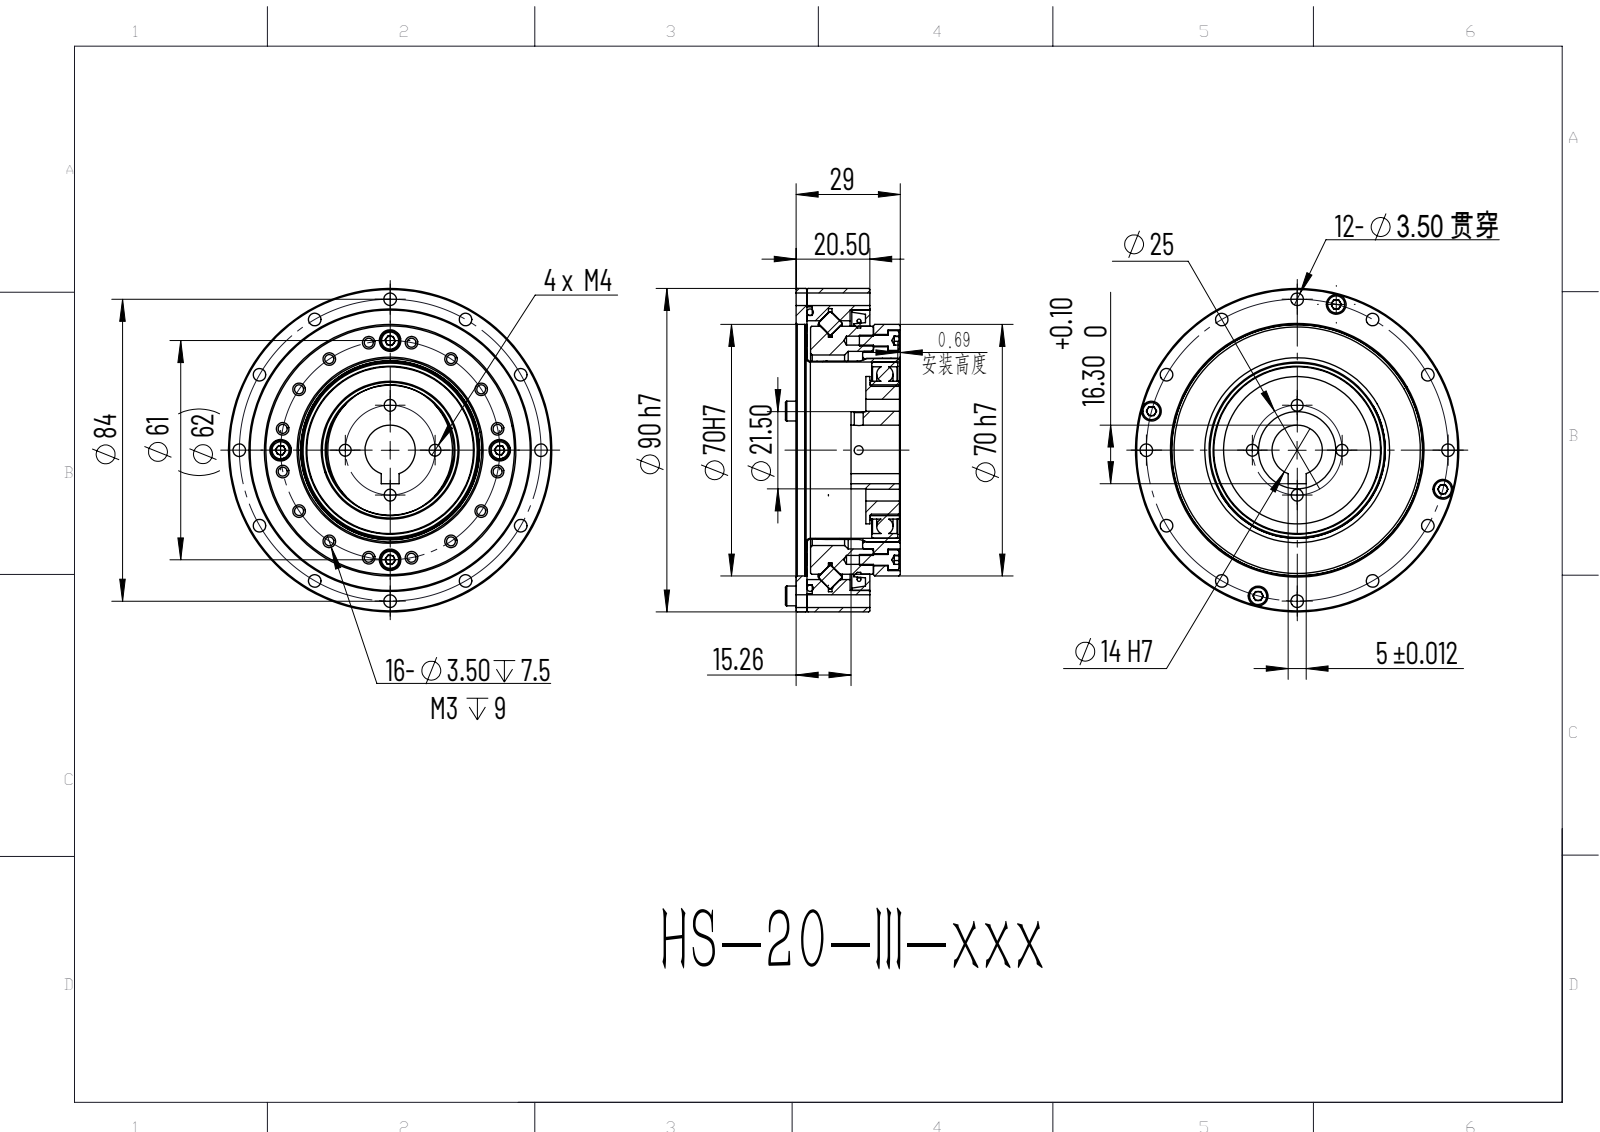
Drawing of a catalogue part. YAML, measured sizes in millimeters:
part_name: "HS-20-III; hexagon socket head cap screws gb_GB_FASTENER_SCREWS_HSHCS M3X8-C; ????-STXB-20050-01; 20-50??????_?? <1> (+8 more)"
step_written_by: "ONSHAPE BY PTC INC, 1.201 (AP242_MANAGED_MODEL_BASED_3D_ENGINEERING_MIM_LF)"
units: millimeters
bodies: {solids: 91, faces: 976, planar: 545, cylindrical: 246, other: 185}
overall_size: [90, 90, 32]
volume: 98411
surface_area: 82973
round_holes:
  - {diameter: 3.5, count: 32}
  - {diameter: 2.5, count: 24}
  - {diameter: 3.3, count: 4}
  - {diameter: 3.4, count: 4}
  - {diameter: 6, count: 4}
  - {diameter: 2.05, count: 1}
  - {diameter: 2.9, count: 1}
  - {diameter: 5, count: 1}
  - {diameter: 14, count: 1}
  - {diameter: 35.56, count: 1}
  - {diameter: 46.4, count: 1}
  - {diameter: 49.07, count: 1}
round_bosses_or_shafts:
  - {diameter: 5, count: 36}
  - {diameter: 5.5, count: 8}
  - {diameter: 3, count: 8}
  - {diameter: 90, count: 1}
  - {diameter: 75, count: 1}
  - {diameter: 69, count: 1}
  - {diameter: 62.8, count: 1}
  - {diameter: 51.19, count: 1}
partial_cylinders:
  - {radius: 2.52, count: 36}
face_to_face_distances: [1, 17.5, 3, 18.5, 20.5, 21.5, 18.76, 4, 2.74, 17.76]
hole_center_spacings: [42, 30.5, 21.74, 72.74, 81.13, 23.34, 16.38, 31.7]
